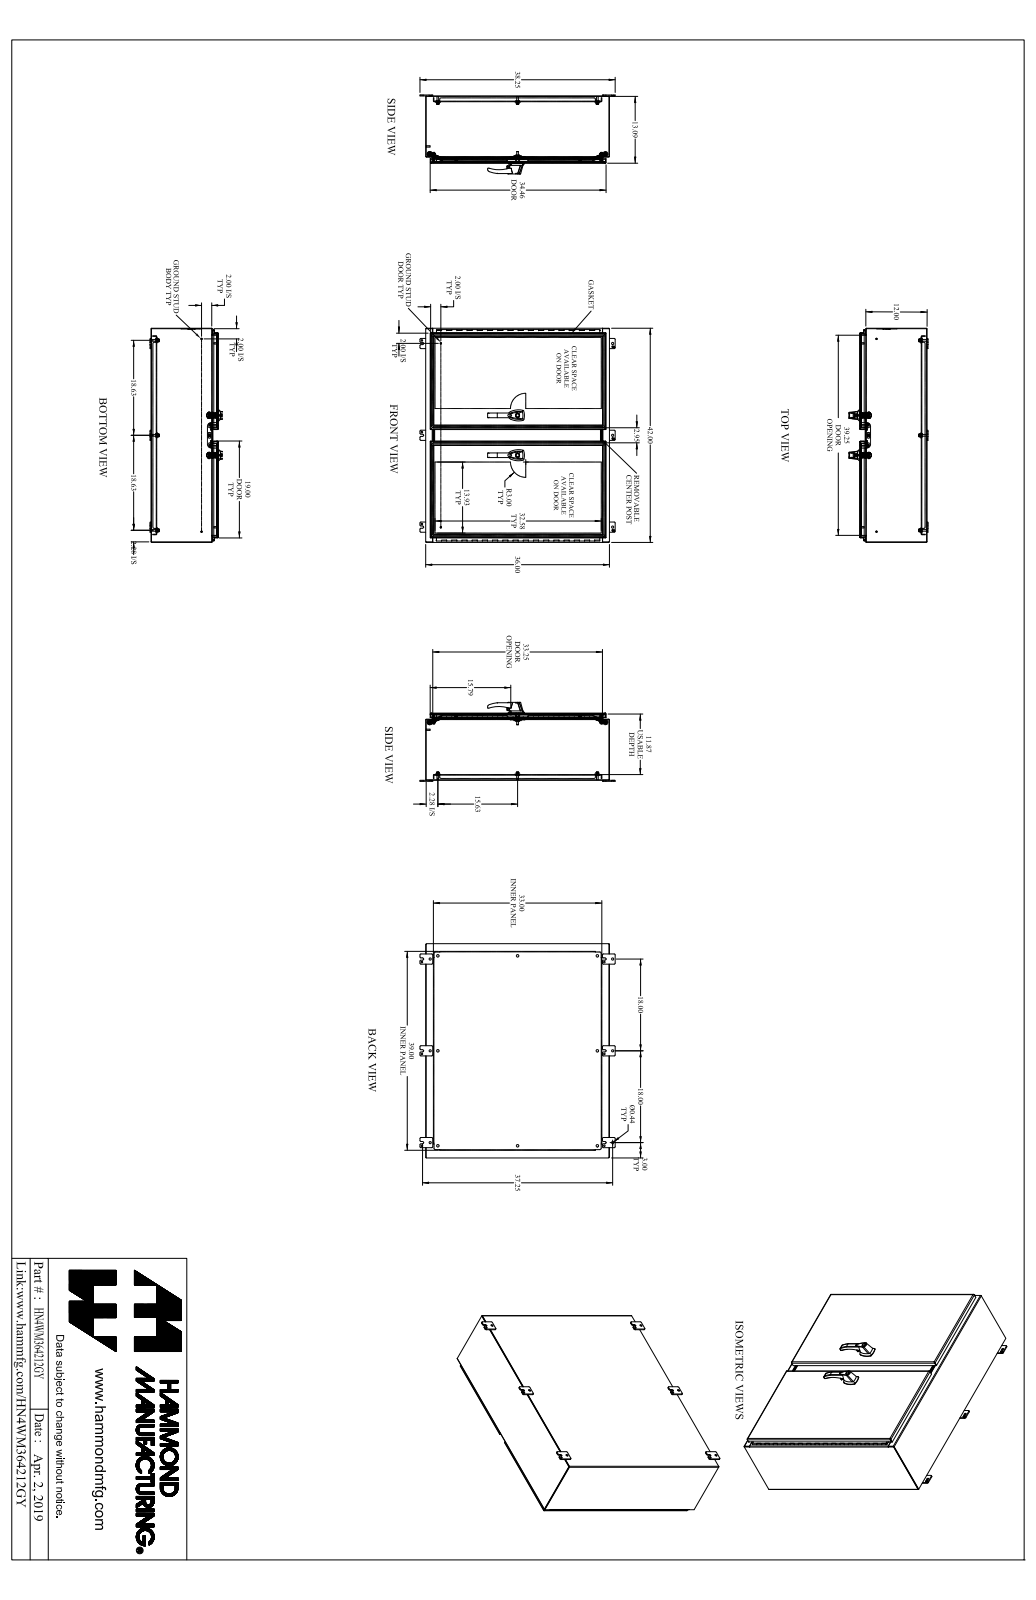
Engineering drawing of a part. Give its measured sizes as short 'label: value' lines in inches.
name: HN4WM364212GY
written by: SolidWorks 2018 (AUTOMOTIVE_DESIGN)
unit: in
bodies: 110 solids, 2952 faces (1387 planar, 1281 cylindrical, 284 other)
size: 42 × 38.25 × 15.487
volume: 729 in³; area: 15 087 in²
holes: 12× ⌀0.304, 8× ⌀0.307, 8× ⌀0.445, 8× ⌀0.5, 6× ⌀0.313, 5× ⌀0.25, 4× ⌀0.281, 4× ⌀0.313, 4× ⌀0.39, 3× ⌀0.201, 3× ⌀0.437, 2× ⌀0.11
bosses: 10× ⌀1, 8× ⌀0.65, 8× ⌀0.375, 8× ⌀0.33, 8× ⌀0.281, 4× ⌀0.75, 4× ⌀0.625, 4× ⌀0.44
rounds: 35× R0.125, 34× R0.25, 32× R0.018, 26× R0.188, 20× R0.06, 17× R0.048, 17× R0.143, 17× R0.5
face distances: 0.095, 1.032, 0.095, 13.09, 12.995, 0.937, 13.185, 13.09, 1.127, 11.963
hole spacings: 6, 40.588, 15.625, 12, 41.897, 18, 21.465, 40.142
